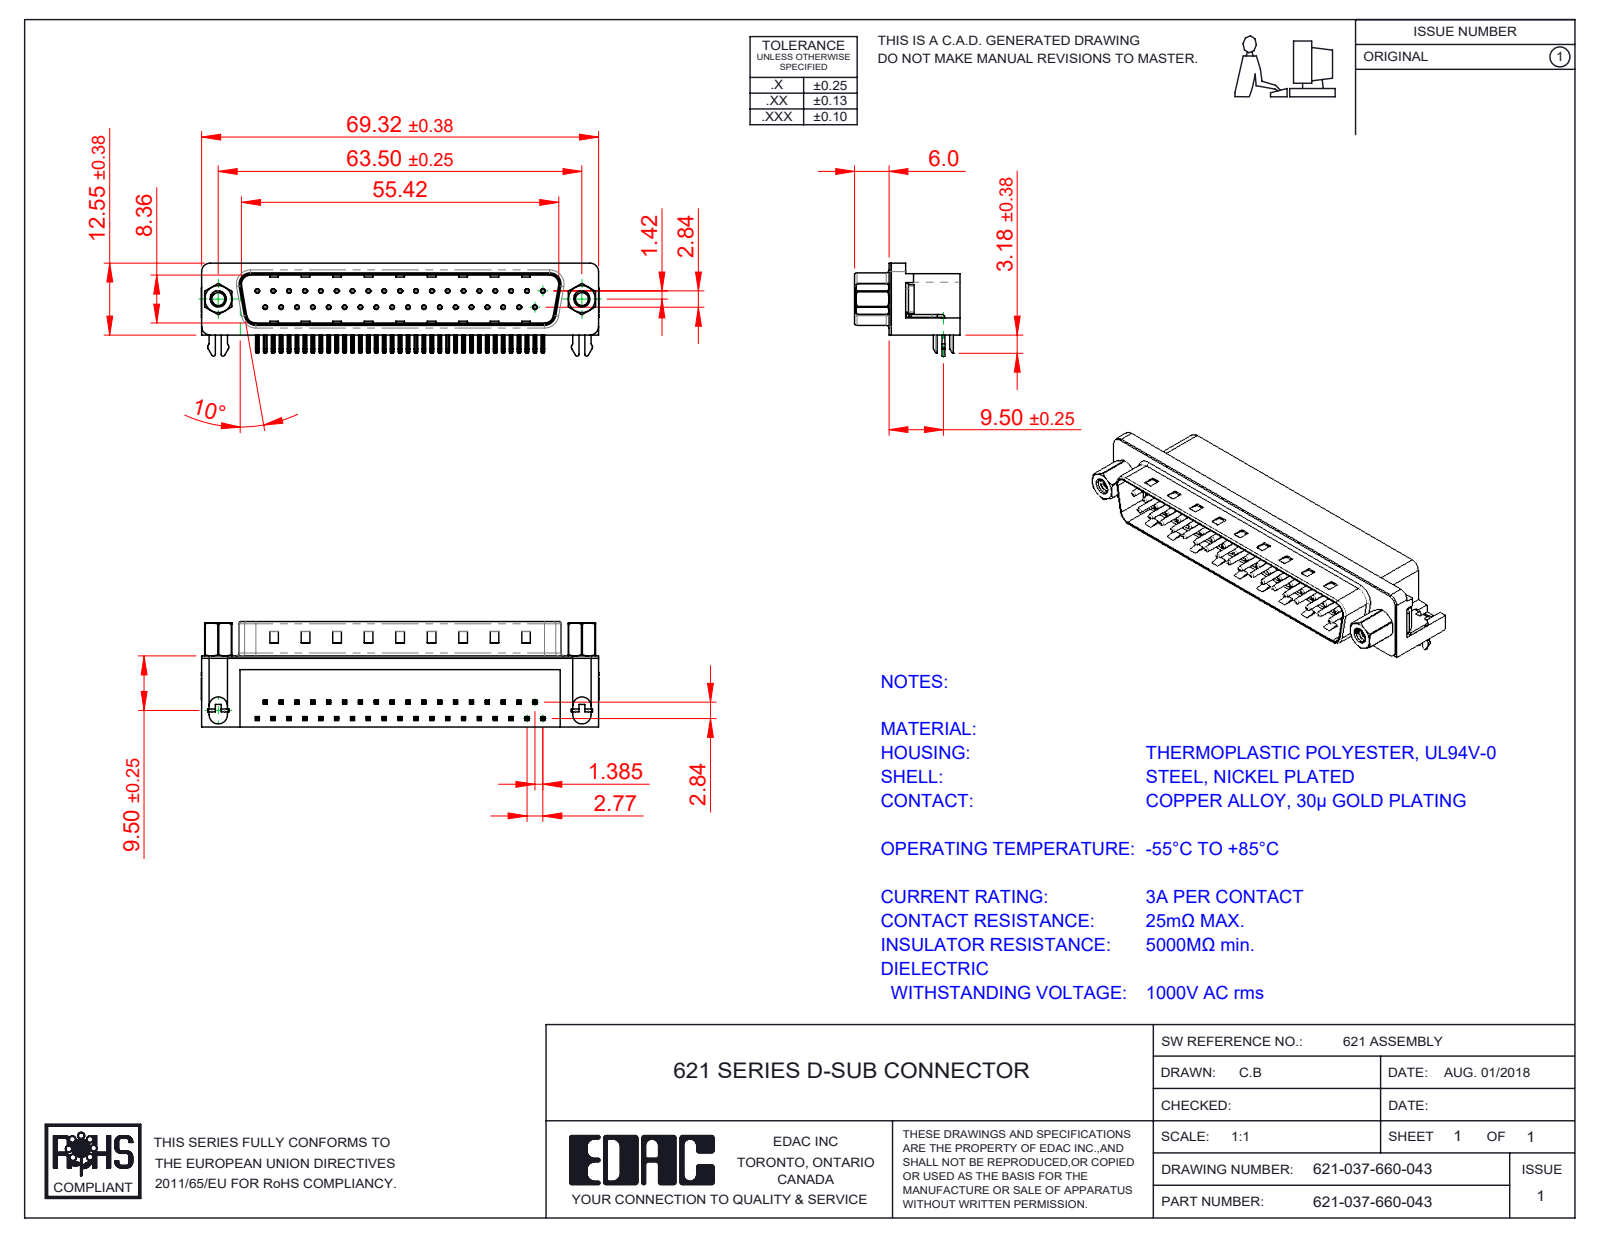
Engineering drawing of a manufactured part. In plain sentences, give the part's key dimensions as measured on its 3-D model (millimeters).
The part is named "621 4 Prong Board Lock; 621-037-660-043; 621 4-40 Hex Standoff 5; 621 Contact Top (+4 more)". Its 3-D file was written by "SolidWorks 2016 (CONFIG_CONTROL_DESIGN)". It is 45 solids with 3445 faces: 2077 planar, 993 cylindrical and 375 other. Overall it measures 69.4 by 18.4 by 16.25 millimeters. Its volume is 8 844 cubic millimeters and its surface area 10 652 square millimeters. Round holes: 37 of diameter 0.35, 37 of diameter 0.8, 2 of diameter 2, 2 of diameter 2.26, 2 of diameter 2.29, 2 of diameter 4, 2 of diameter 4.8, 2 of diameter 5. Round bosses or shafts: 37 of diameter 0.75, 2 of diameter 4.9, 2 of diameter 4.75, 2 of diameter 3.9, 2 of diameter 3, 2 of diameter 2.79. Partial cylindrical surfaces (rounded edges, fillets, slot ends): 160 of radius 0.25, 74 of radius 0.12, 16 of radius 1, 9 of radius 0.5, 8 of radius 1.6, 7 of radius 1.5, 4 of radius 0.9, 4 of radius 2. The main face-to-face distances are 0.4, 12, 10.35, 8.76, 2.1, 1.7, 10.46, 10.86, 12.4, 9. The hole center spacings are 3.16, 2.77, 5.54, 8.31, 11.08, 13.85, 19.39, 22.16.
